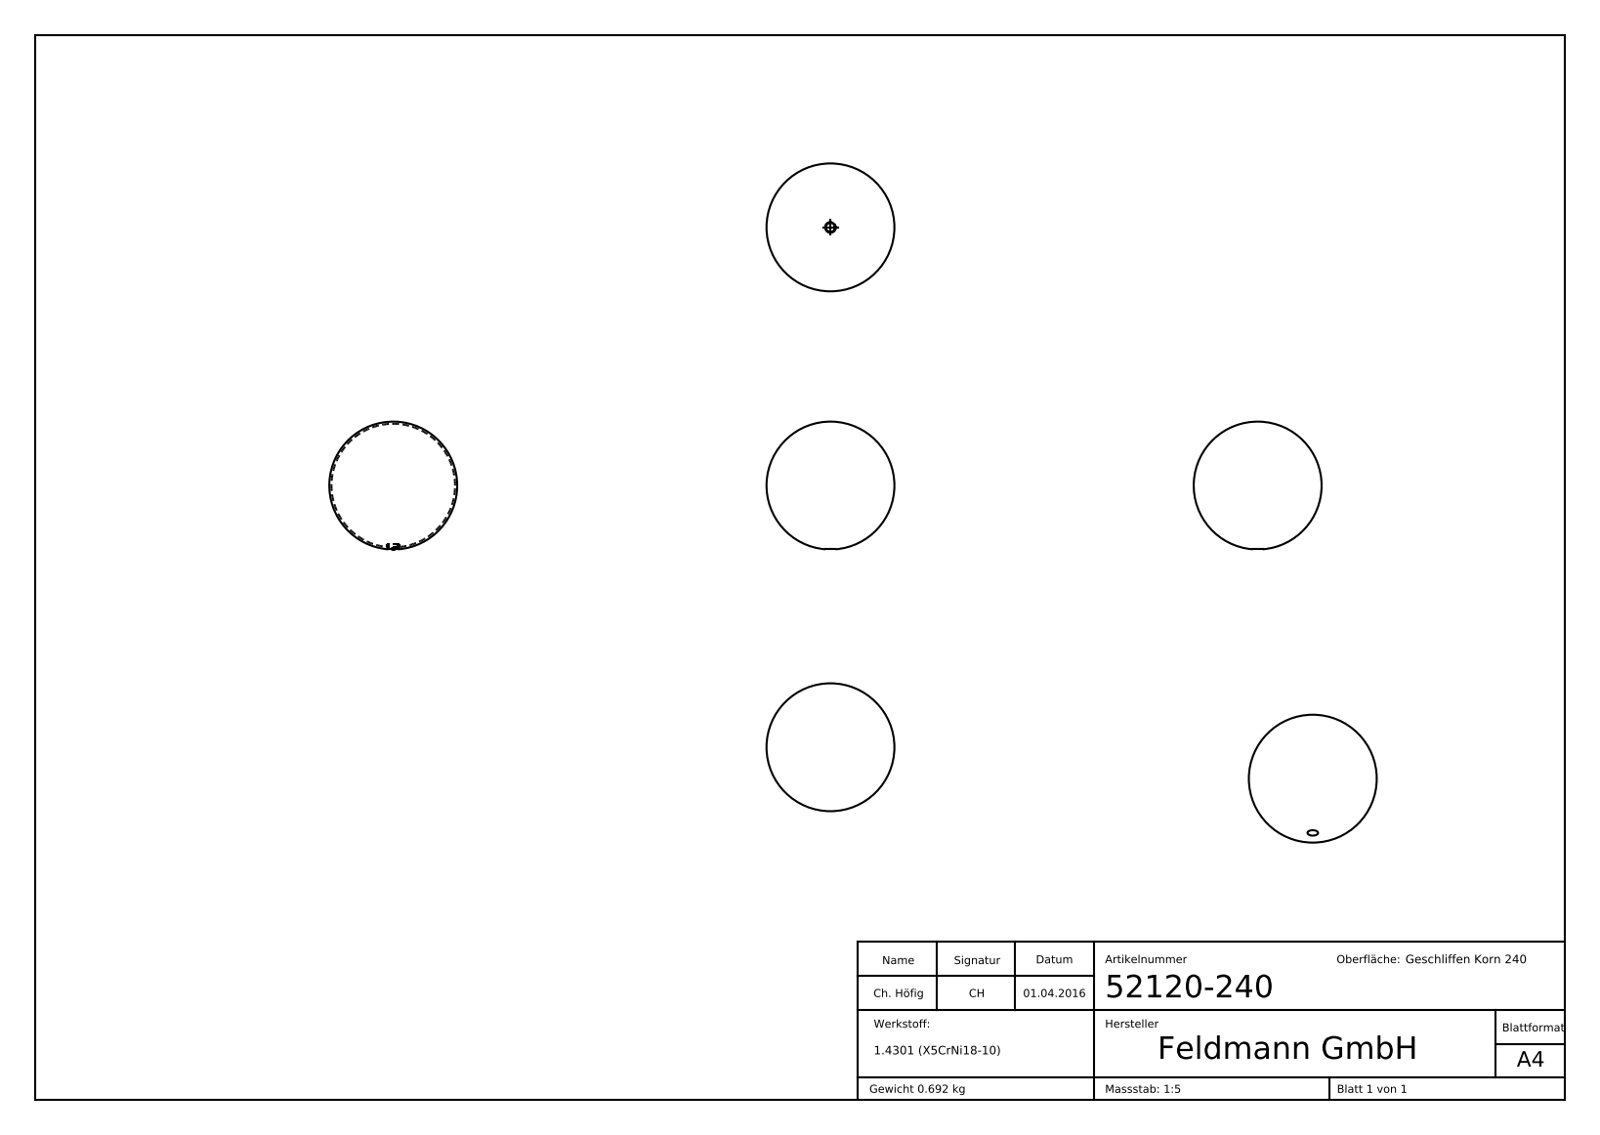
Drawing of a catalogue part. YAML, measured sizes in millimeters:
part_name: "52120-240"
step_written_by: "SolidWorks 2015 (CONFIG_CONTROL_DESIGN)"
units: millimeters
bodies: {solids: 1, faces: 227, planar: 102, cylindrical: 4, other: 121}
overall_size: [120, 120, 119.81]
volume: 87545
surface_area: 87636
round_holes:
  - {diameter: 8.5, count: 1}
round_bosses_or_shafts:
  - {diameter: 12, count: 1}
